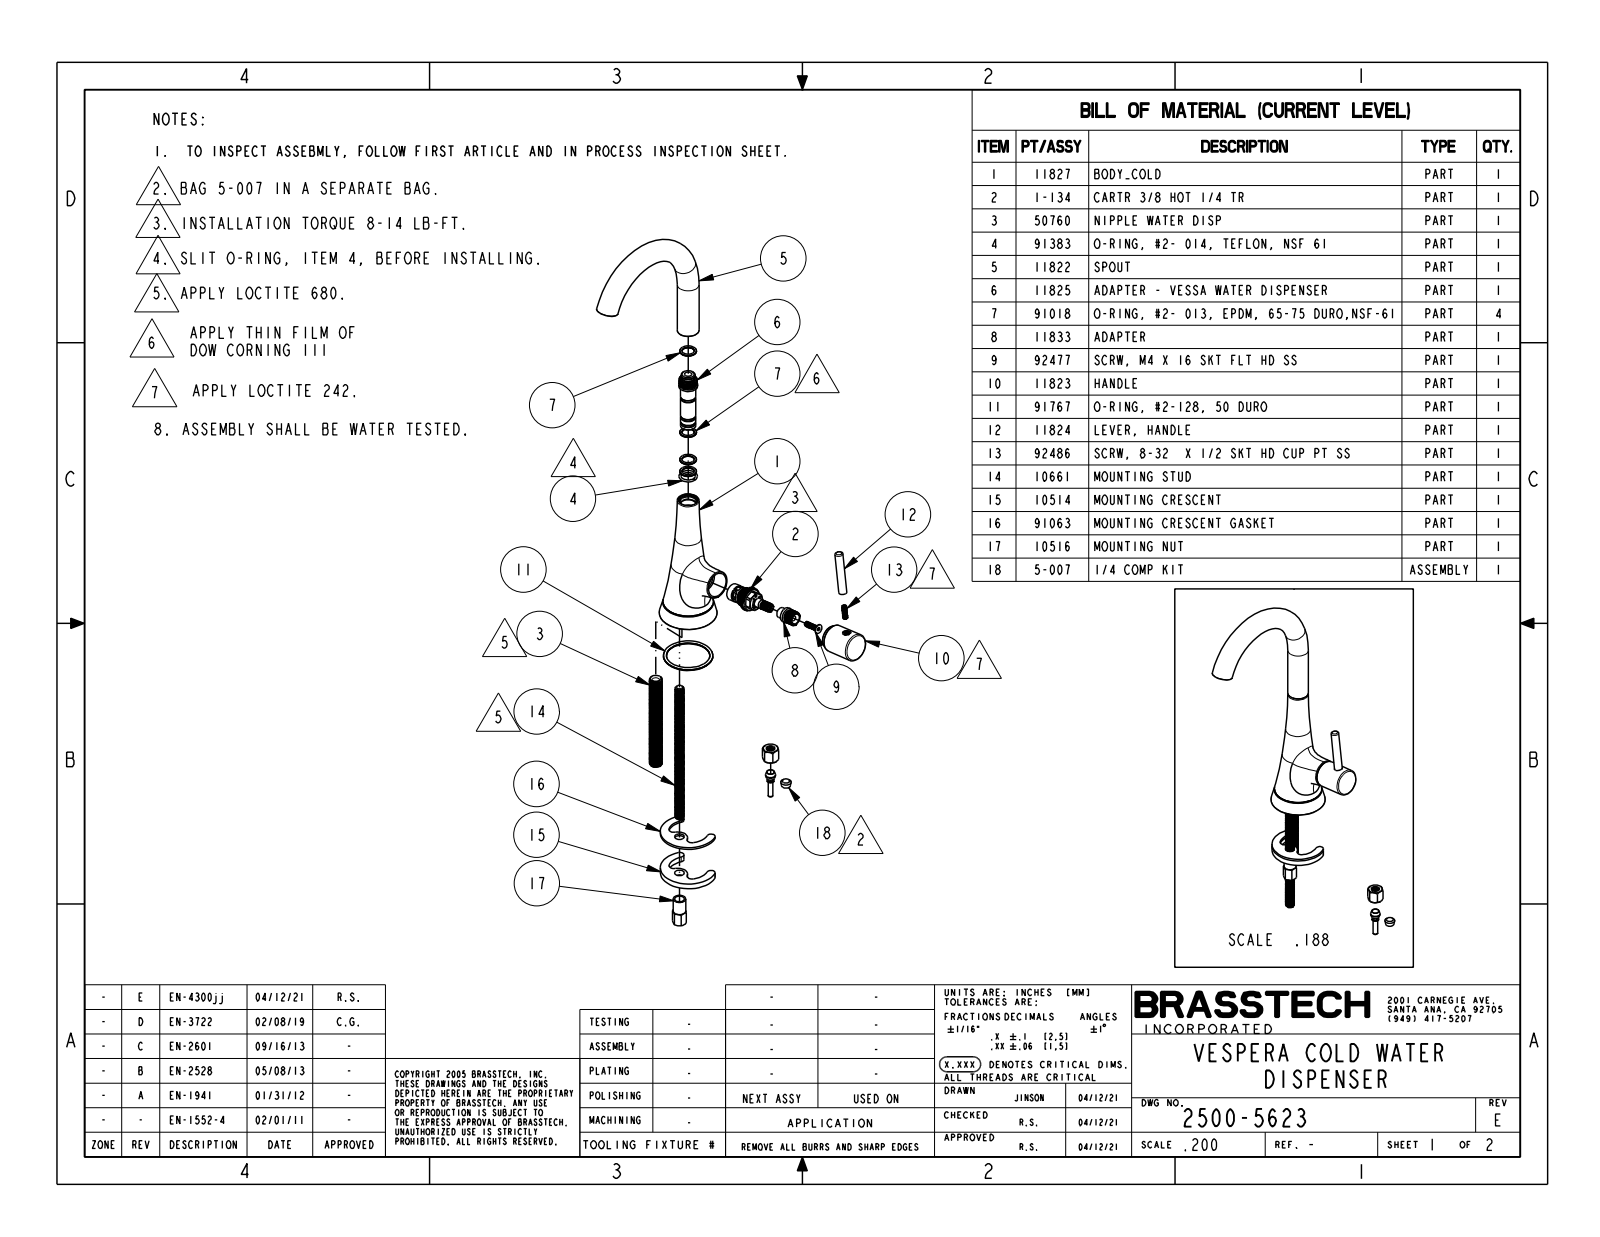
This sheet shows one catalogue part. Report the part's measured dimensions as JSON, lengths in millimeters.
{"part_name": "2500-5623", "step_written_by": "CREO PARAMETRIC BY PTC INC, 2018400 (CONFIG_CONTROL_DESIGN)", "units": "millimeters", "bodies": {"solids": 1, "faces": 63, "planar": 9, "cylindrical": 14, "other": 40}, "overall_size": [236.5, 134, 91], "volume_mm3": 176700, "surface_area_mm2": 30700, "round_holes": [[7.4, 1]], "round_bosses_or_shafts": [[43.7, 1], [24.4, 1], [20.7, 1], [19.1, 1], [15.9, 1], [7.1, 1]], "face_to_face_distances": [28.7, 121.5, 121.2, 0.4, 0.5, 28.2, 39.6]}
